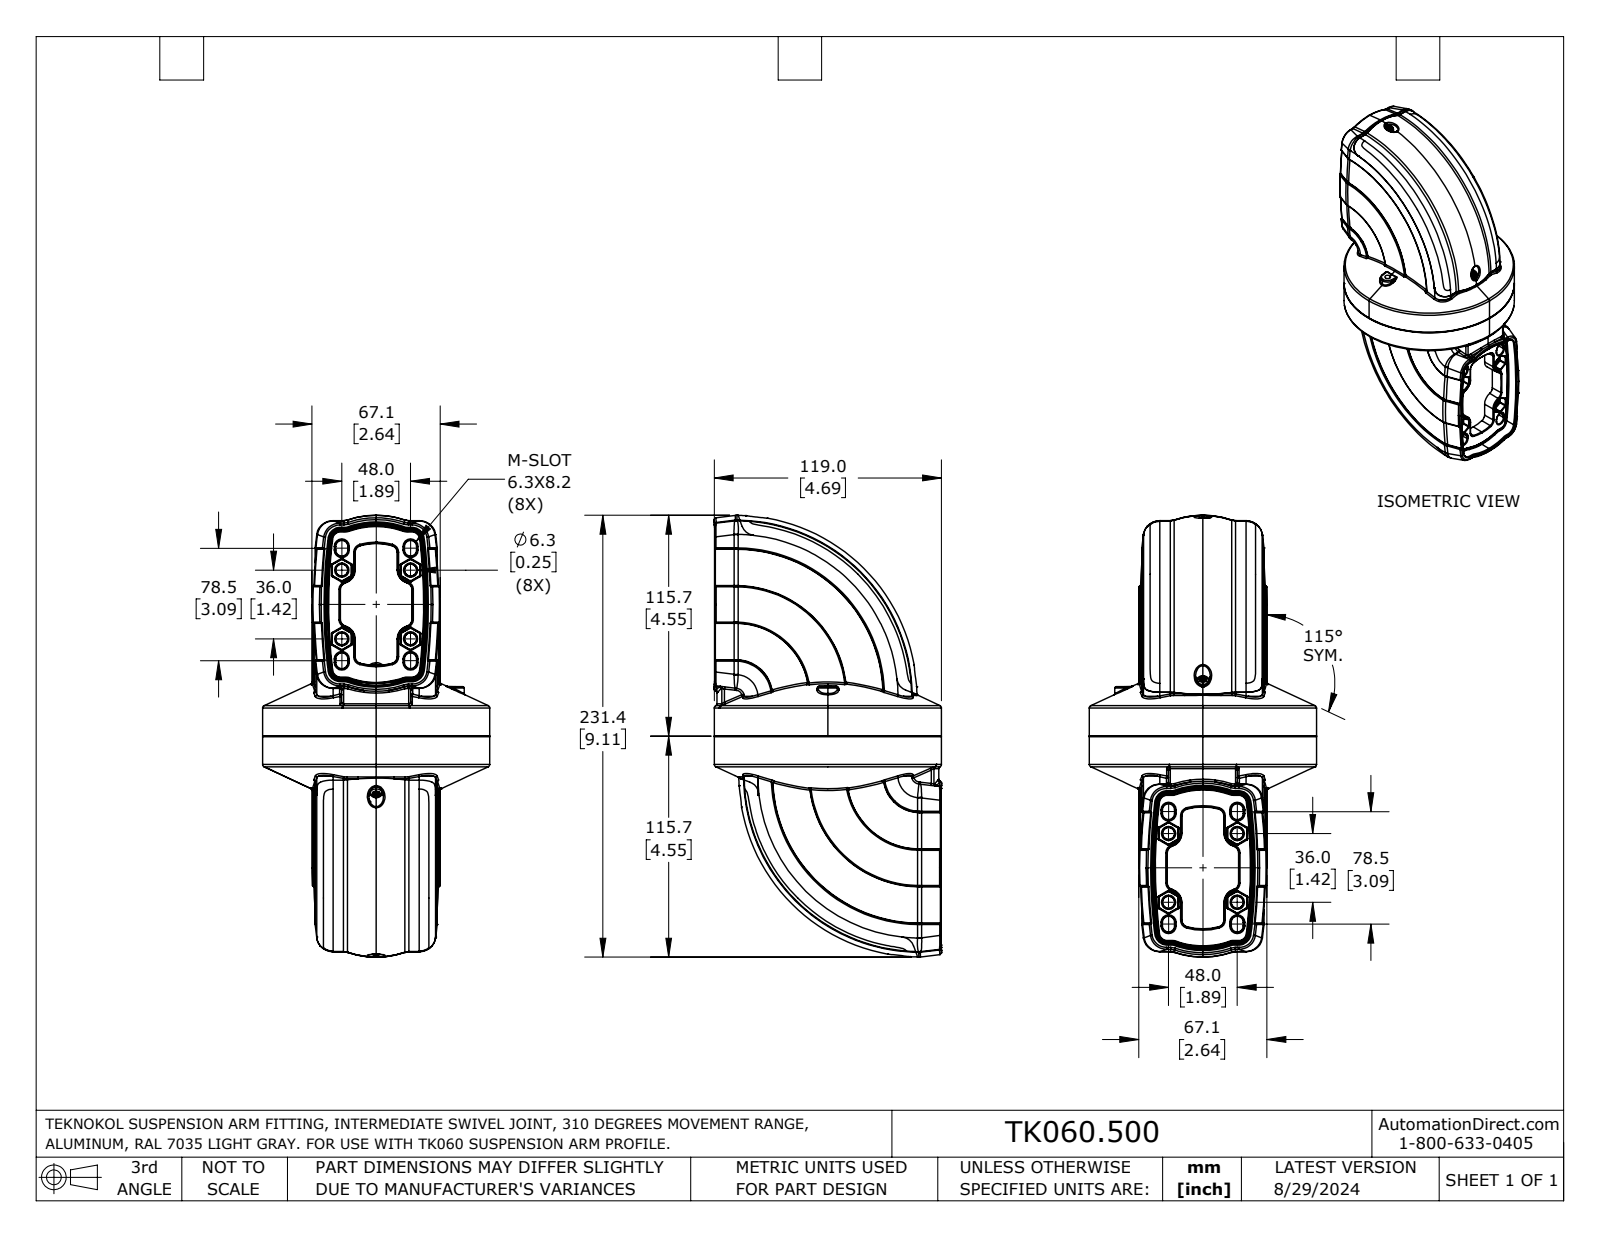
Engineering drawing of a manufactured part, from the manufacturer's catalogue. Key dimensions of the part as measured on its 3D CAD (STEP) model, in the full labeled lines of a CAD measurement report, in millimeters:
Part name (STEP PRODUCT): TK060.500_REV6
STEP written by: SolidWorks 2023 (AUTOMOTIVE_DESIGN)
Units: millimetres
Bodies: 1 solid, 2021 faces (263 planar, 355 cylindrical, 1403 other)
Overall size (bounding box): 231.4 × 119.2 × 119
Volume: 1 006 000 mm³ · Surface area: 134 800 mm²
Round holes (diameter × count): ⌀5 ×2, ⌀6 ×2, ⌀4 ×1, ⌀44 ×1, ⌀93.1 ×1, ⌀115 ×1
Round bosses / shafts (diameter × count): ⌀119 ×1, ⌀113 ×1, ⌀90.7 ×1, ⌀74.6 ×1
Partial cylindrical surfaces — rounded edges, fillets, slot ends (radius × count): R0.5 ×56, R0.4 ×40, R2.4 ×32, R0.2 ×24, R1 ×8, R1 ×8, R1.4 ×6, R0.4 ×5
Main face-to-face distances: 0.5, 19.6, 20.1, 14.3, 5.3, 5.8, 9.2, 95.5, 96, 104.6
Hole centre spacings: 41, 41, 82, 82, 82
